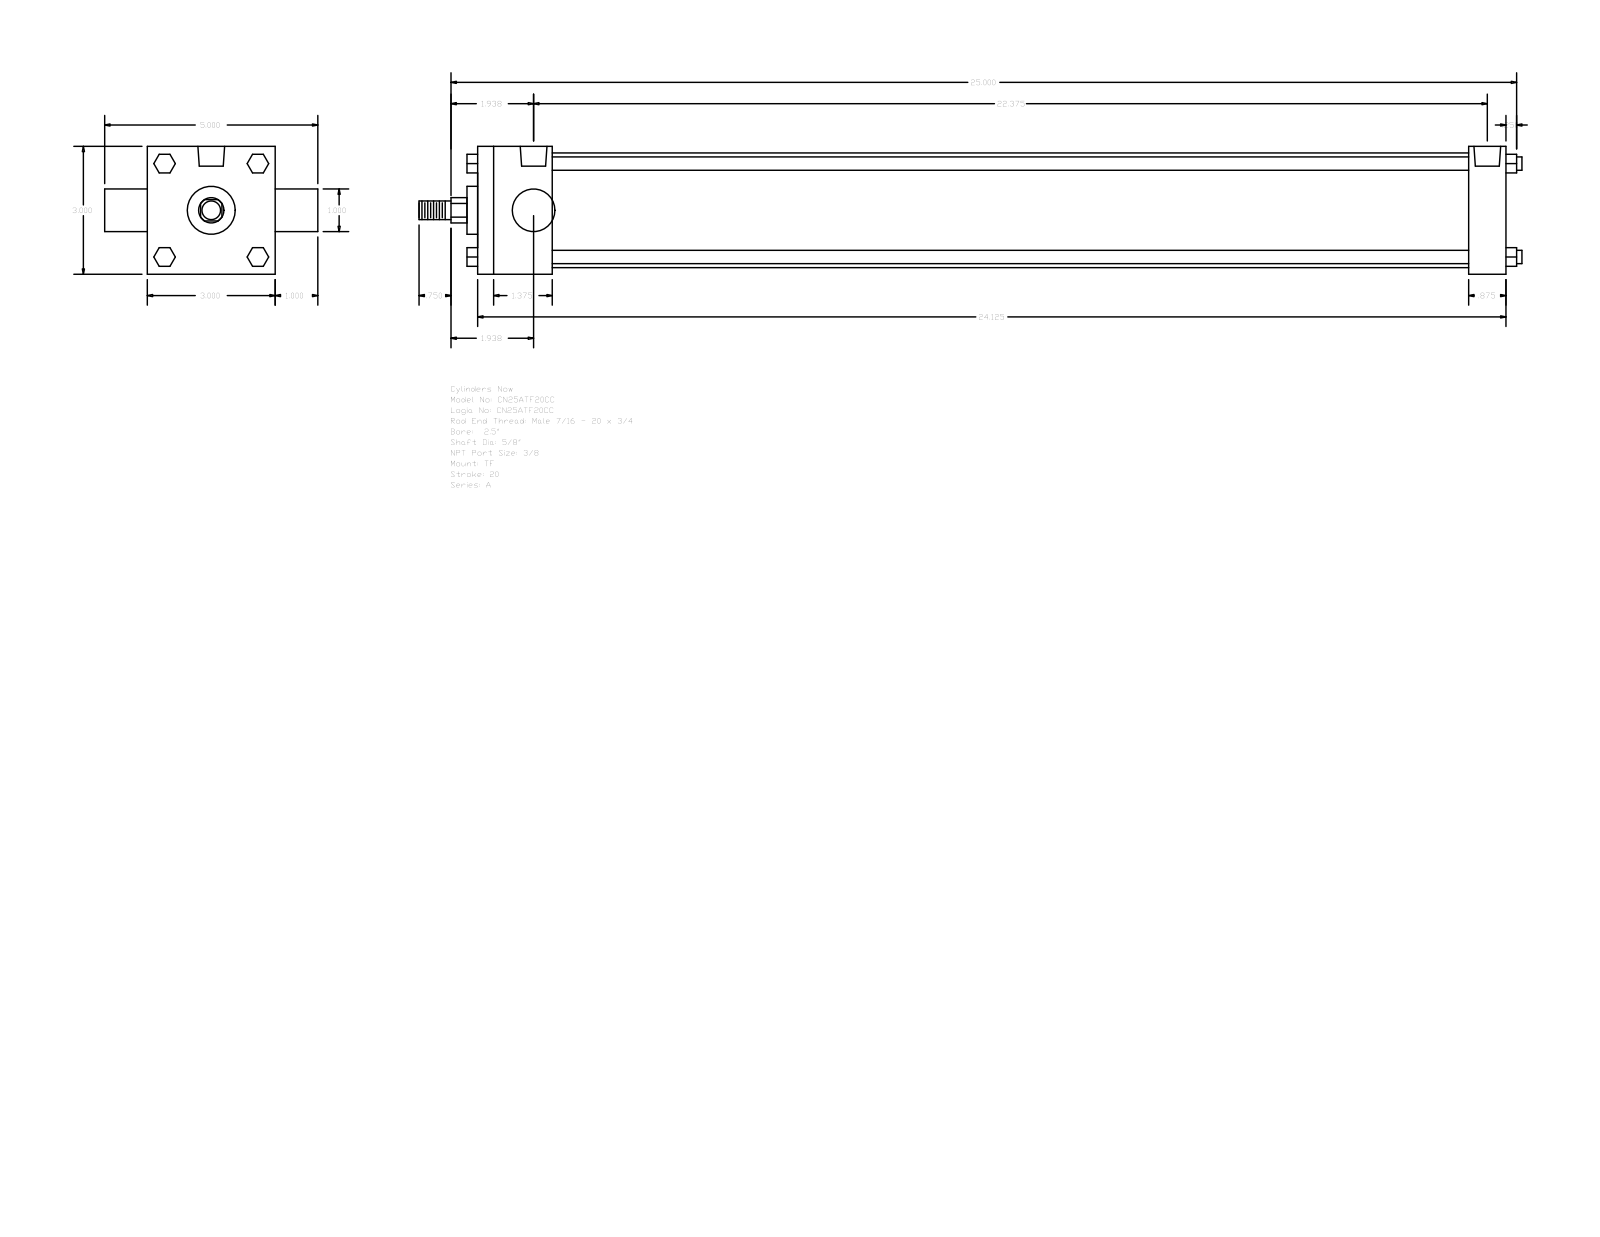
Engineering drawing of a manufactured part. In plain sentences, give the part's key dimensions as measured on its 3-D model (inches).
The part is named "A_TF__0250_0.625". Its 3-D file was written by "GSSL Pune (CONFIG_CONTROL_DESIGN)". It is 0 solids with 120 faces: 92 planar, 28 cylindrical and 0 other. Overall it measures 25.875 by 5 by 3 inches. Round holes: 3 of diameter 0.219, 2 of diameter 0.627. Round bosses or shafts: 4 of diameter 0.313, 1 of diameter 2.69, 1 of diameter 1.125, 1 of diameter 1, 1 of diameter 0.625, 1 of diameter 0.437. Partial cylindrical surfaces (rounded edges, fillets, slot ends): 1 of radius 0.297. The main face-to-face distances are 3, 24.125, 1.75, 23.25, 21.5, 22.375, 0.875, 1, 4, 0.25. The hole center spacings are 0.094, 22.469, 22.375, 22.563.
